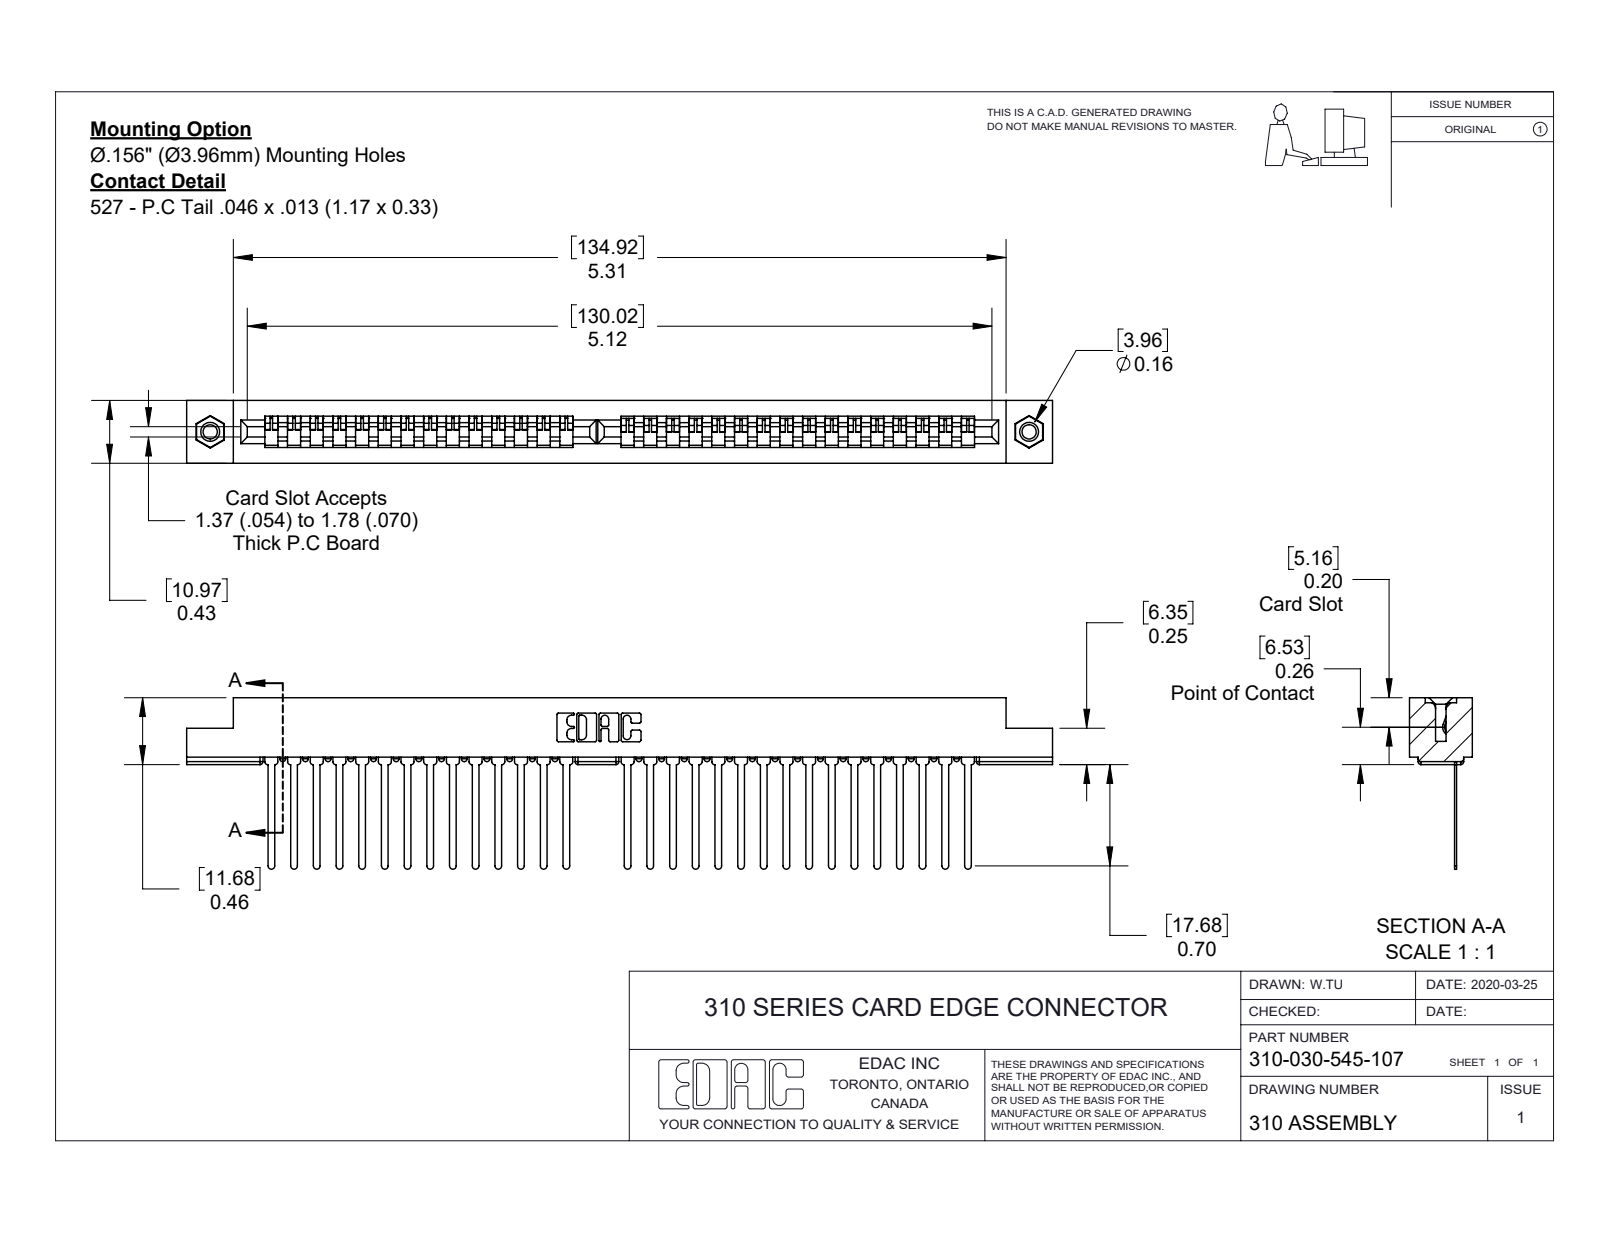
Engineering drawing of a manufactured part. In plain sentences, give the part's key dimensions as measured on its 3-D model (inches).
The part is named "310 Part_.116 Hex; 345-250-001_345-250-005-103; 307-290-001_545; 310-030-545-107". Its 3-D file was written by "SolidWorks 2016 (CONFIG_CONTROL_DESIGN)". It is 33 solids with 1906 faces: 1226 planar, 600 cylindrical and 80 other. Overall it measures 5.953 by 1.179 by 0.432 inches. Its volume is 0.78 cubic inches and its surface area 24.78 square inches. Round holes: 2 of diameter 0.098, 2 of diameter 0.125, 2 of diameter 0.156. Round bosses or shafts: 2 of diameter 0.155. Partial cylindrical surfaces (rounded edges, fillets, slot ends): 158 of radius 0.02, 30 of radius 0.023, 22 of radius 0.01, 6 of radius 0.007, 6 of radius 0.031, 3 of radius 0.026, 2 of radius 0.012, 2 of radius 0.025. The main face-to-face distances are 0.109, 0.324, 0.015, 0.013, 0.432, 0.072, 0.124, 0.309, 0.2, 0.187. The hole center spacings are 5.63.
